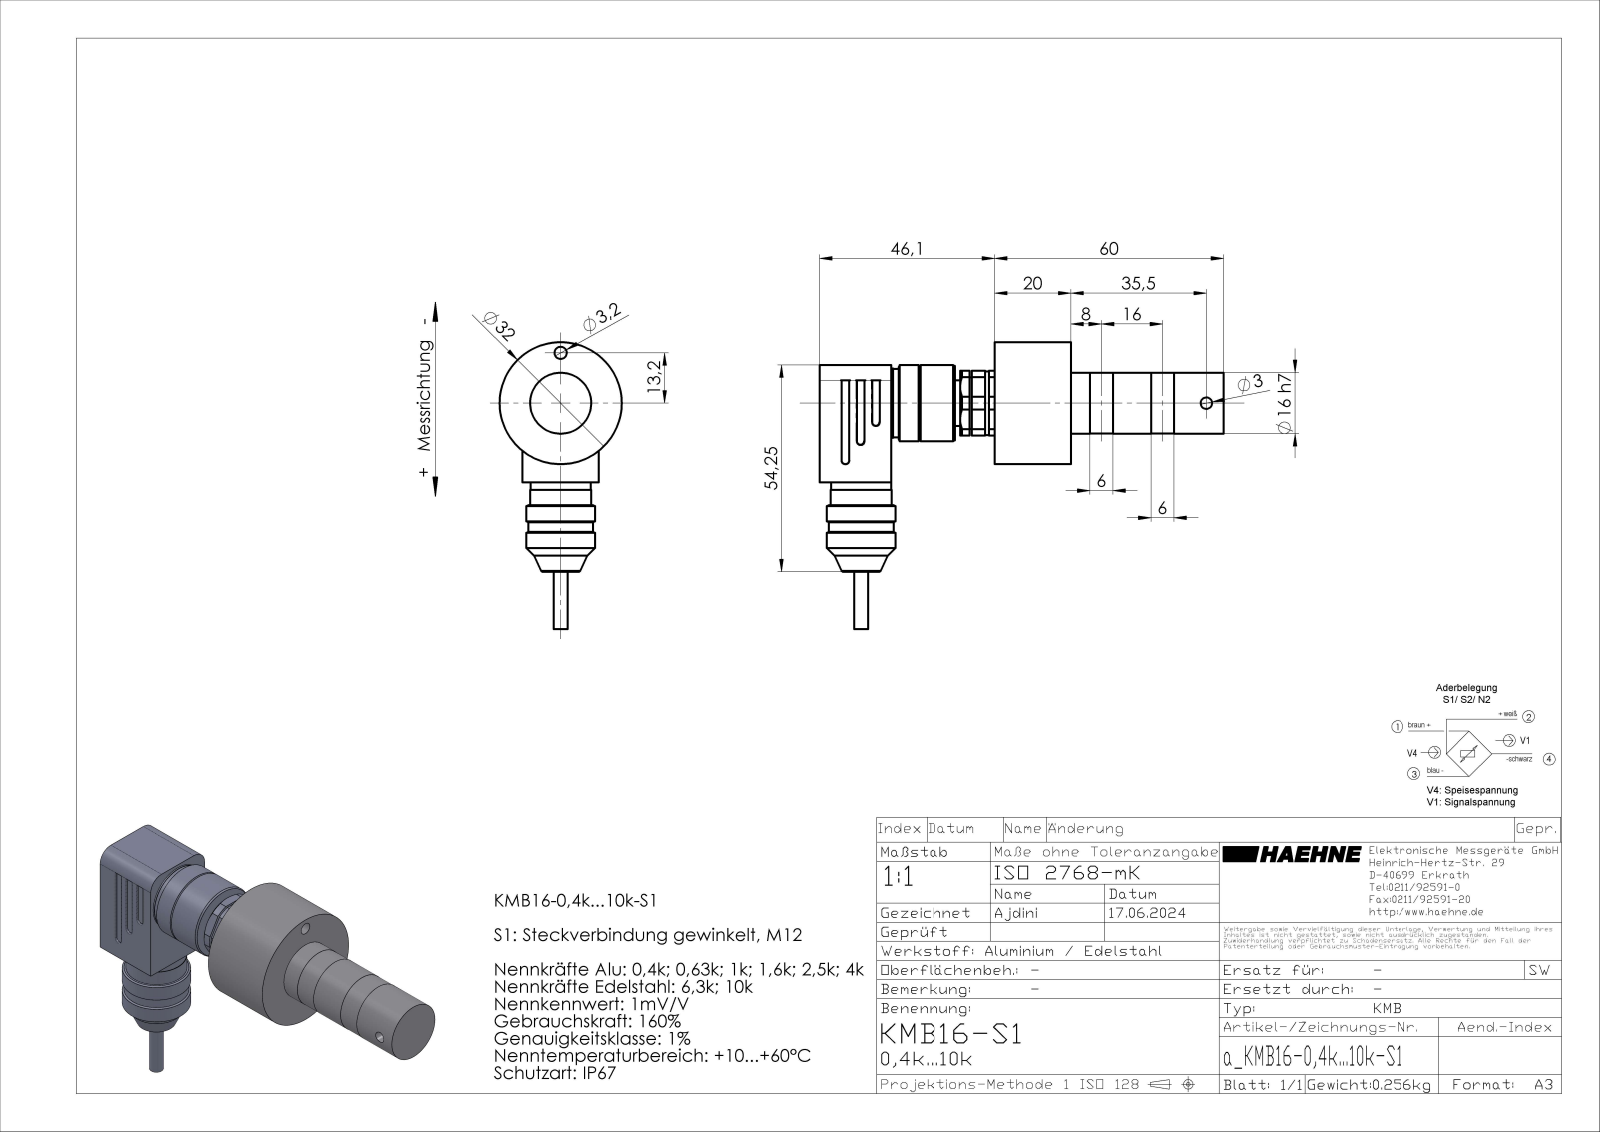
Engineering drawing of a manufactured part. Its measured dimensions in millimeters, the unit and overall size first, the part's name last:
Units: millimetres
Overall size (bounding box): 106.1 × 75.25 × 32
Round holes (diameter × count): ⌀3 ×1, ⌀3.2 ×1, ⌀4.5 ×1, ⌀6 ×1, ⌀8.37 ×1, ⌀12 ×1, ⌀15 ×1
Round bosses / shafts (diameter × count): ⌀1.5 ×4, ⌀1 ×4, ⌀18 ×2, ⌀16 ×2, ⌀32 ×1, ⌀20 ×1, ⌀18.2 ×1, ⌀17 ×1
Partial cylindrical surfaces — rounded edges, fillets, slot ends (radius × count): R0.2 ×12, R1 ×11, R0.3 ×6, R4 ×2, R0.57 ×1, R0.65 ×1, R0.77 ×1, R3.5 ×1
Main face-to-face distances: 20, 46.1, 66.1, 18.75, 27.35, 47.35, 30.75, 0.5, 20.7, 1.95
Hole centre spacings: 13.2
Volume: 47 905 mm³ · Surface area: 15 836 mm²
Bodies: 5 solids, 261 faces (114 planar, 108 cylindrical, 39 other)
Part name (STEP PRODUCT): Kabel Durchm 3,7; X02163Z1 Einschraubstecker M16x1,5 EC-FSD4-0,5_16 8027469; X02156Z1+X02163Z1 Zusammenbau; KMB16-0,4k...4k-T alu (+2 more)
STEP written by: SolidWorks 2023 (CONFIG_CONTROL_DESIGN)
